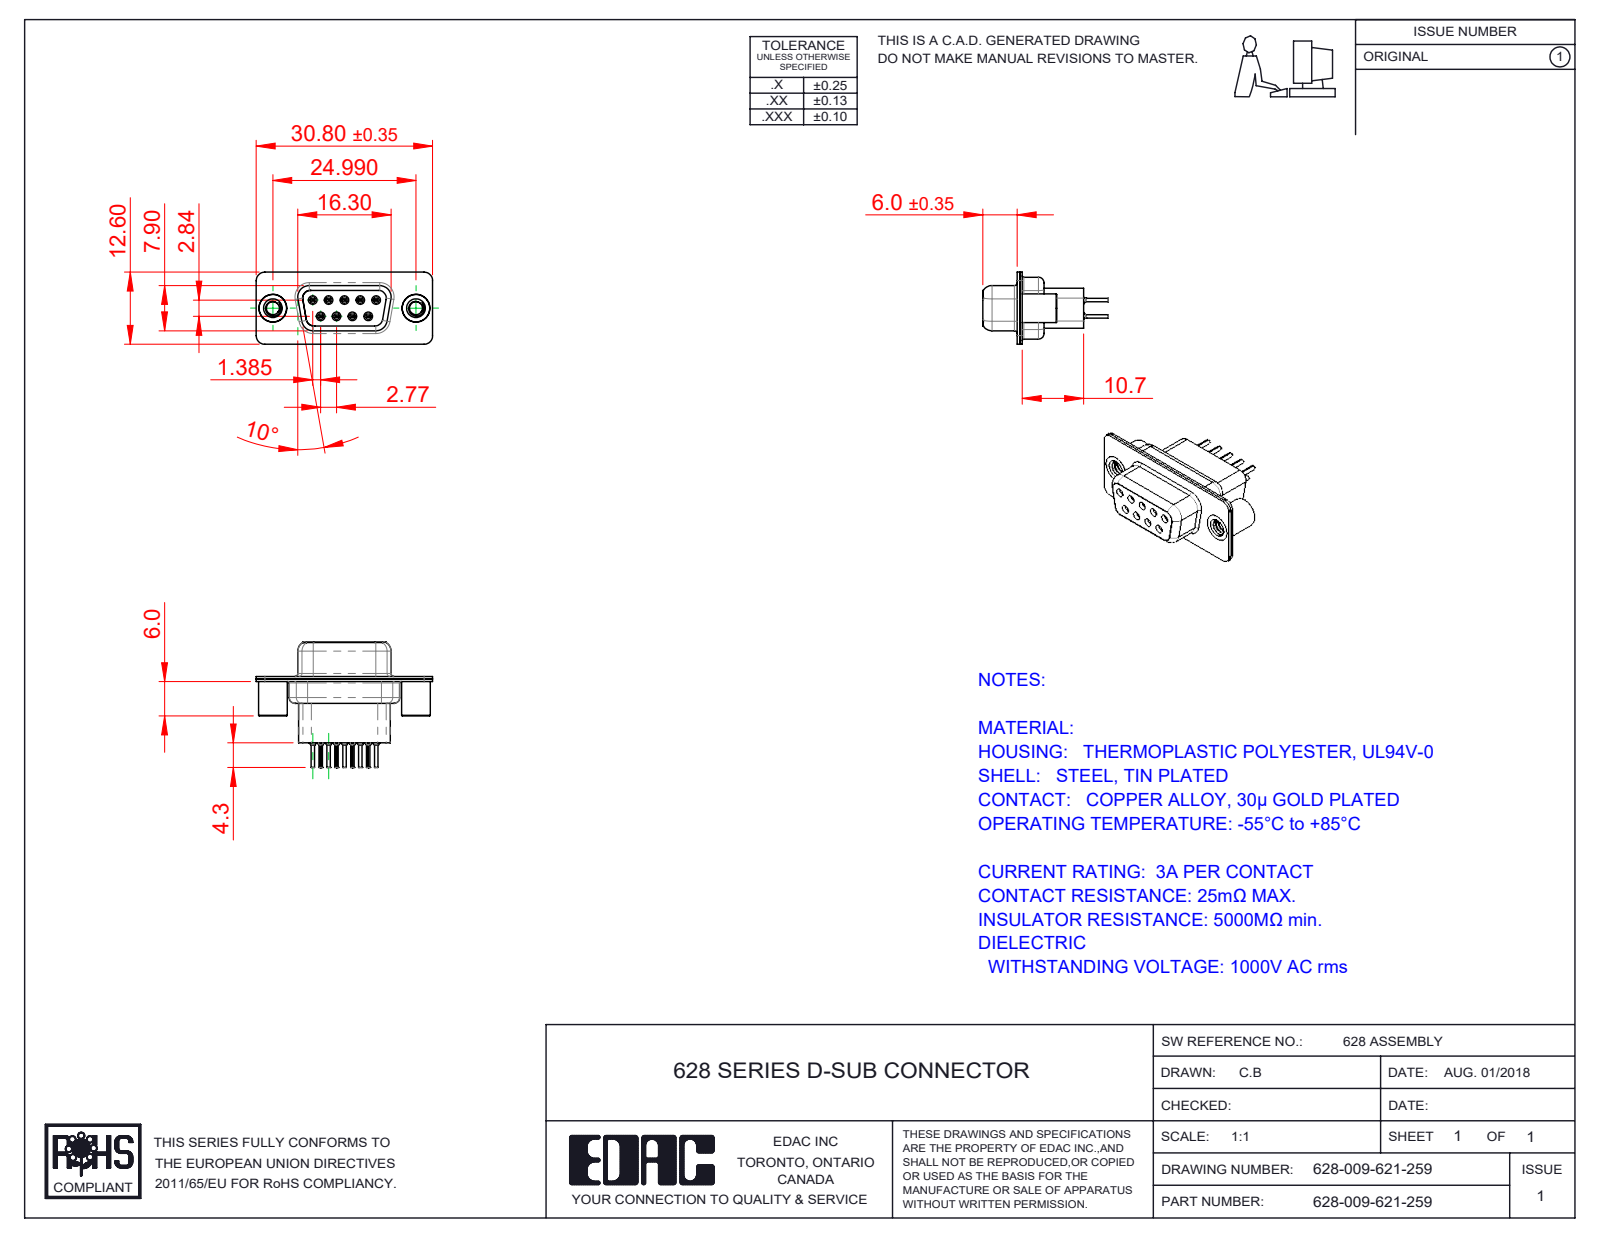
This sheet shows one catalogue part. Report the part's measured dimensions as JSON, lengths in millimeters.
{"part_name": "628 Shell Front_09 Contacts; 628 Contact Row 1_21H; 628 Shell Rear_09 Contacts; 628 4-40 Threaded Standoff BS (+3 more)", "step_written_by": "SolidWorks 2020 (CONFIG_CONTROL_DESIGN)", "units": "millimeters", "bodies": {"solids": 14, "faces": 1408, "planar": 346, "cylindrical": 454, "other": 608}, "overall_size": [30.8, 21.9, 12.6], "volume_mm3": 2328, "surface_area_mm2": 5525, "round_holes": [[0.2, 9], [0.8, 9], [0.9, 9], [1.1, 9], [1.6, 9], [1.7, 5], [2.26, 2], [4, 2], [4.05, 2], [4.85, 2]], "round_bosses_or_shafts": [[2, 9], [1.5, 9], [1.2, 9], [0.6, 9], [5, 2], [4.95, 2], [4.8, 2]], "partial_cylinders_radius": [[0.1, 18], [1.5, 17], [2, 12], [0.28, 9], [1.35, 6], [0.25, 4], [0.5, 4], [0.6, 4]], "face_to_face_distances": [0.45, 0.4, 0.9, 8.5, 6.6, 1.9, 1.4, 7, 6.9, 10.7], "hole_center_spacings": [3.16, 2.77, 5.54, 5.03, 5.04, 8.31, 7.48, 7.49]}
